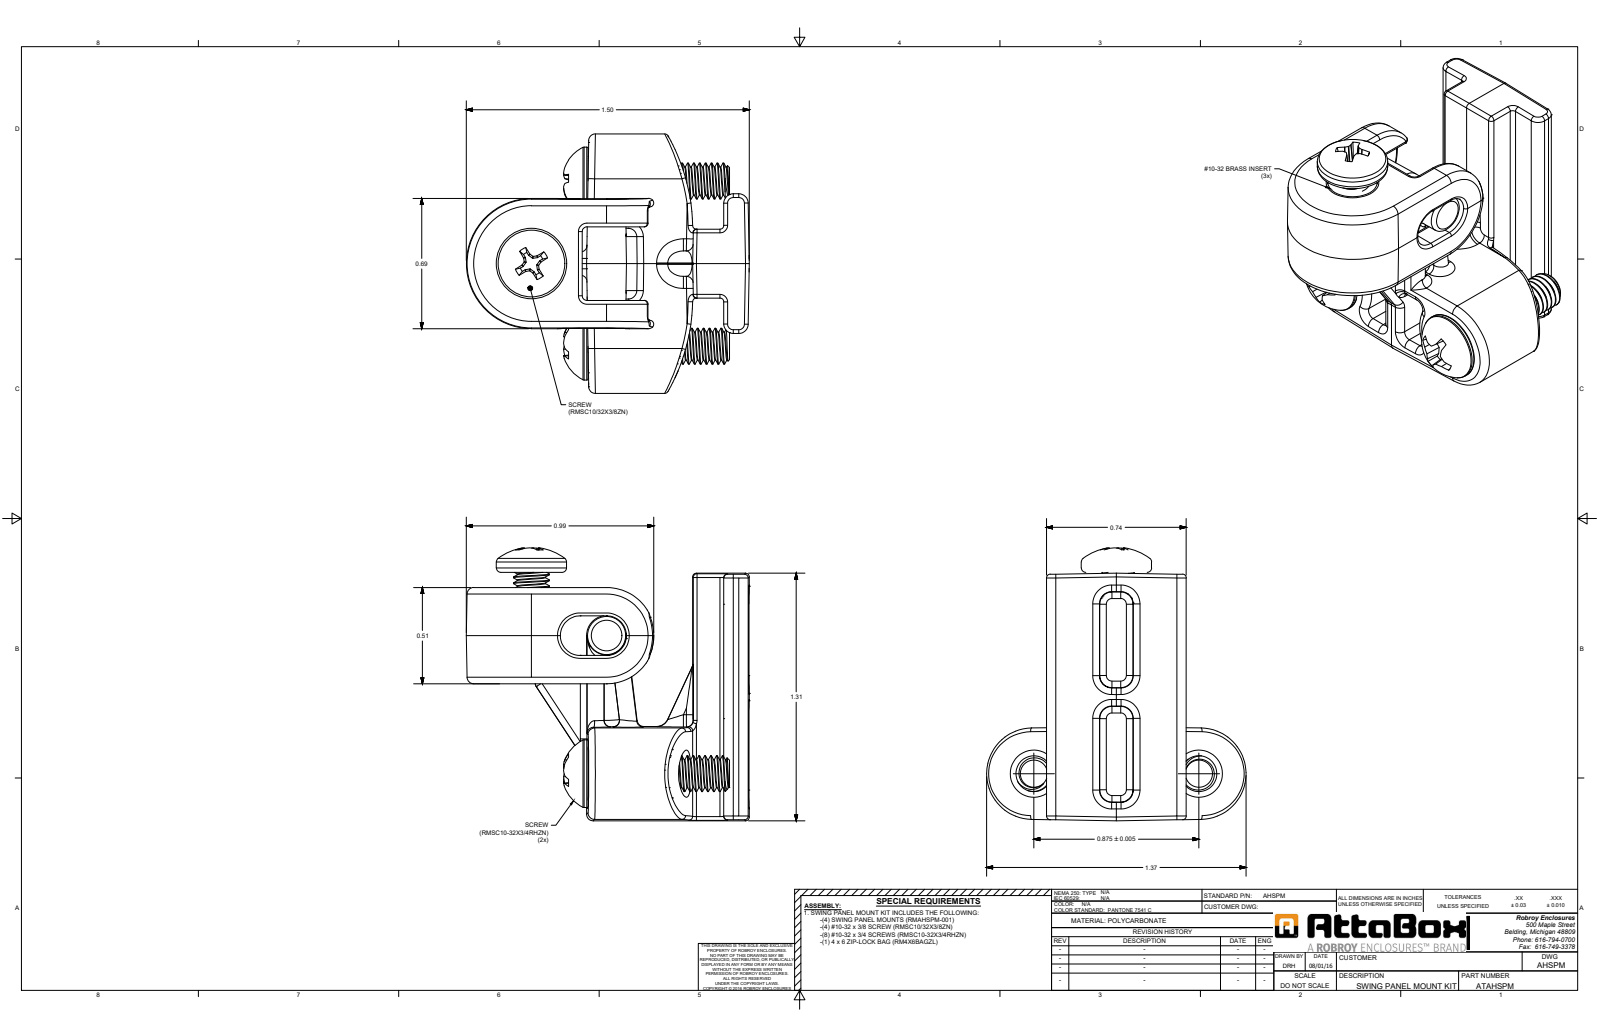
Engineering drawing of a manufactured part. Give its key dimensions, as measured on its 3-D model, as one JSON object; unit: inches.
{"part_name": "AHSPM", "step_written_by": "SolidWorks 2019 (AUTOMOTIVE_DESIGN)", "units": "inches", "bodies": {"solids": 10, "faces": 543, "planar": 142, "cylindrical": 194, "other": 207}, "overall_size": [1.5, 1.447, 1.375], "volume_in3": 0.775, "surface_area_in2": 14.54, "round_holes": [[0.156, 3], [0.25, 3]], "round_bosses_or_shafts": [[0.262, 3], [0.19, 3], [0.359, 2], [0.373, 1]], "partial_cylinders_radius": [[0.035, 66], [0.02, 44], [0.065, 14], [0.004, 12], [0.015, 11], [0.045, 4], [0.05, 4], [0.025, 2]], "face_to_face_distances": [0.863, 0.5, 0.72, 0.51, 0.563, 0.3, 0.69, 0.365, 0.013, 1.313], "hole_center_spacings": [0.875]}
